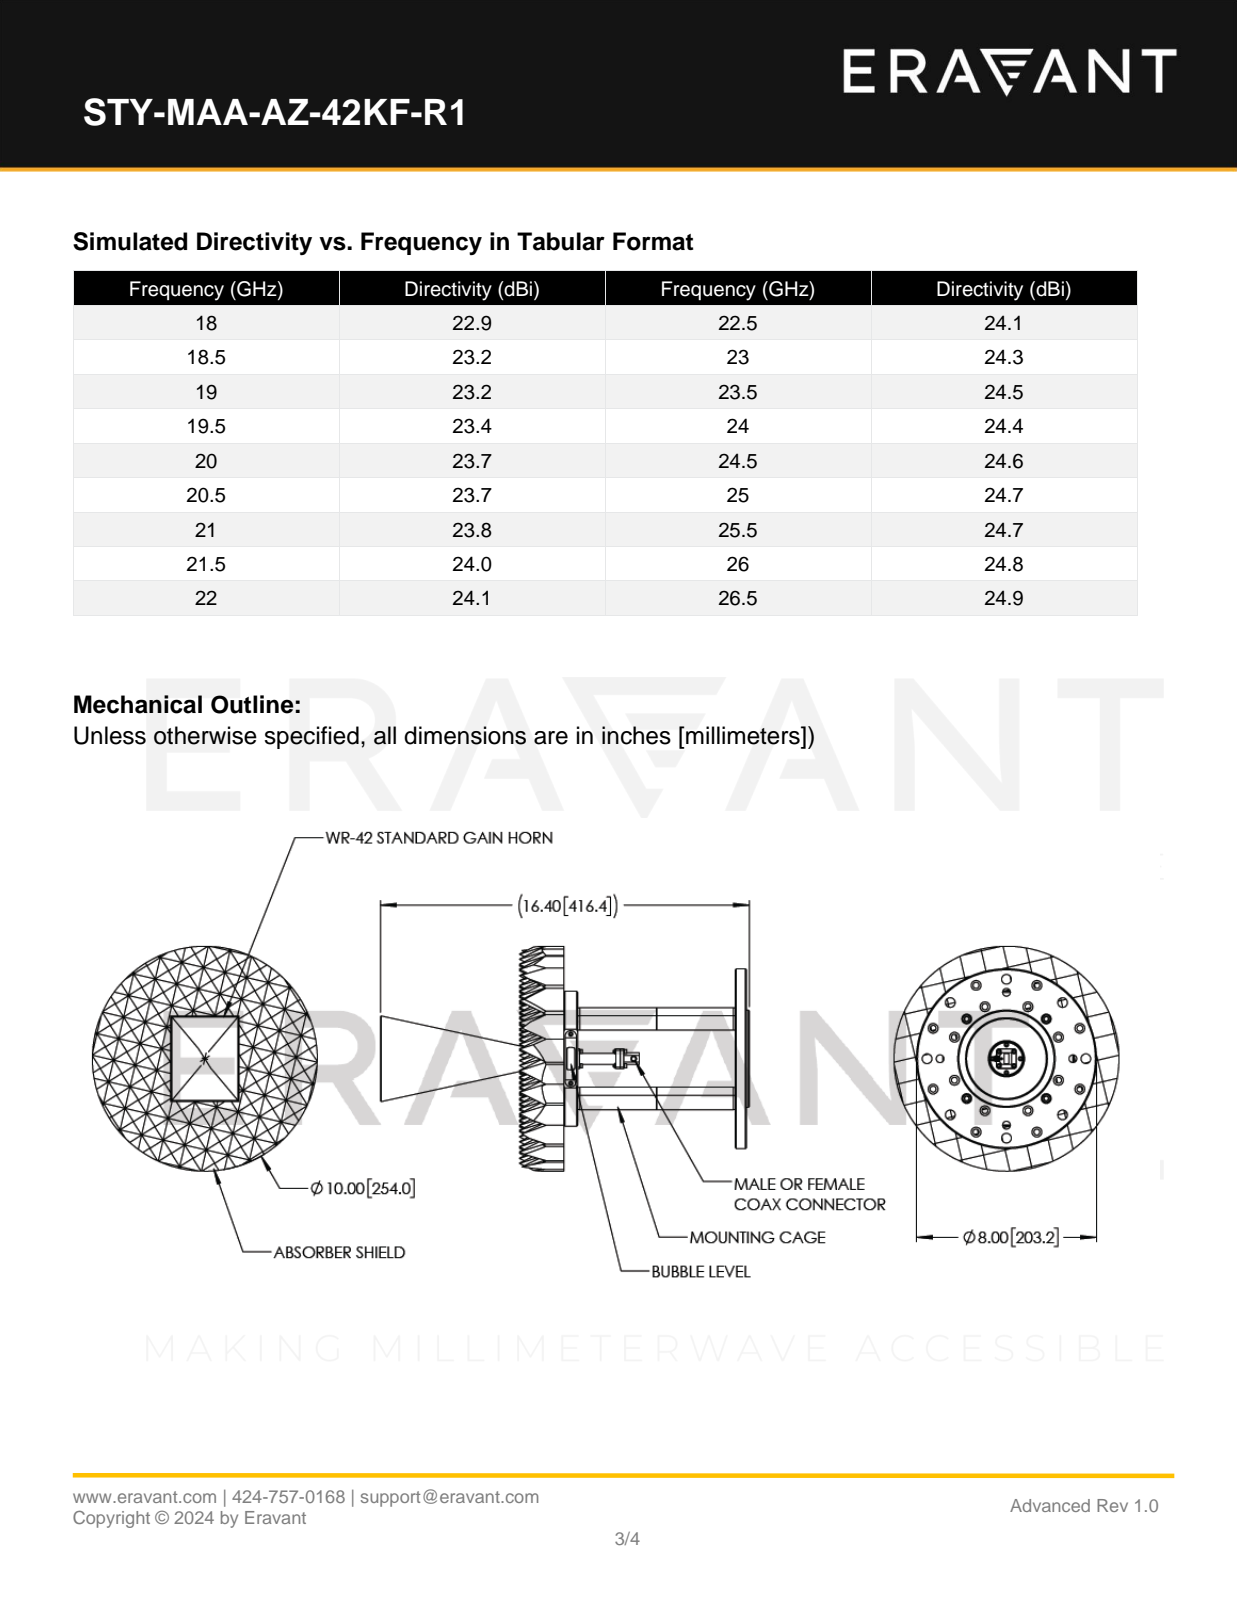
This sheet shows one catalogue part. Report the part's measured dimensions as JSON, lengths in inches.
{"part_name": "STY-MAA-AZ-42KF-R1", "step_written_by": "SolidWorks 2021 (CONFIG_CONTROL_DESIGN)", "units": "inches", "bodies": {"solids": 84, "faces": 1829, "planar": 703, "cylindrical": 459, "other": 667}, "overall_size": [16.396, 10, 10], "volume_in3": 184.7, "surface_area_in2": 830, "round_holes": [[0.266, 20], [0.437, 16], [0.433, 8], [0.12, 4], [0.348, 4], [0.75, 4], [0.089, 2], [0.125, 2], [0.182, 1], [1.55, 1], [3.543, 1]], "round_bosses_or_shafts": [[0.21, 5], [1, 4], [0.437, 4], [0.183, 4], [0.112, 4], [0.08, 4], [10, 1], [8, 1]], "partial_cylinders_radius": [[0.042, 4], [0.106, 4], [0.08, 2], [0.25, 2], [0.24, 1]], "face_to_face_distances": [0.984, 1.969, 0.985, 1.969, 2.953, 3.938, 3.937, 5.906, 2.953, 4.922], "hole_center_spacings": [4.326, 5.585, 3.458, 5.046, 5.918, 1.551, 2.496, 3.53]}
